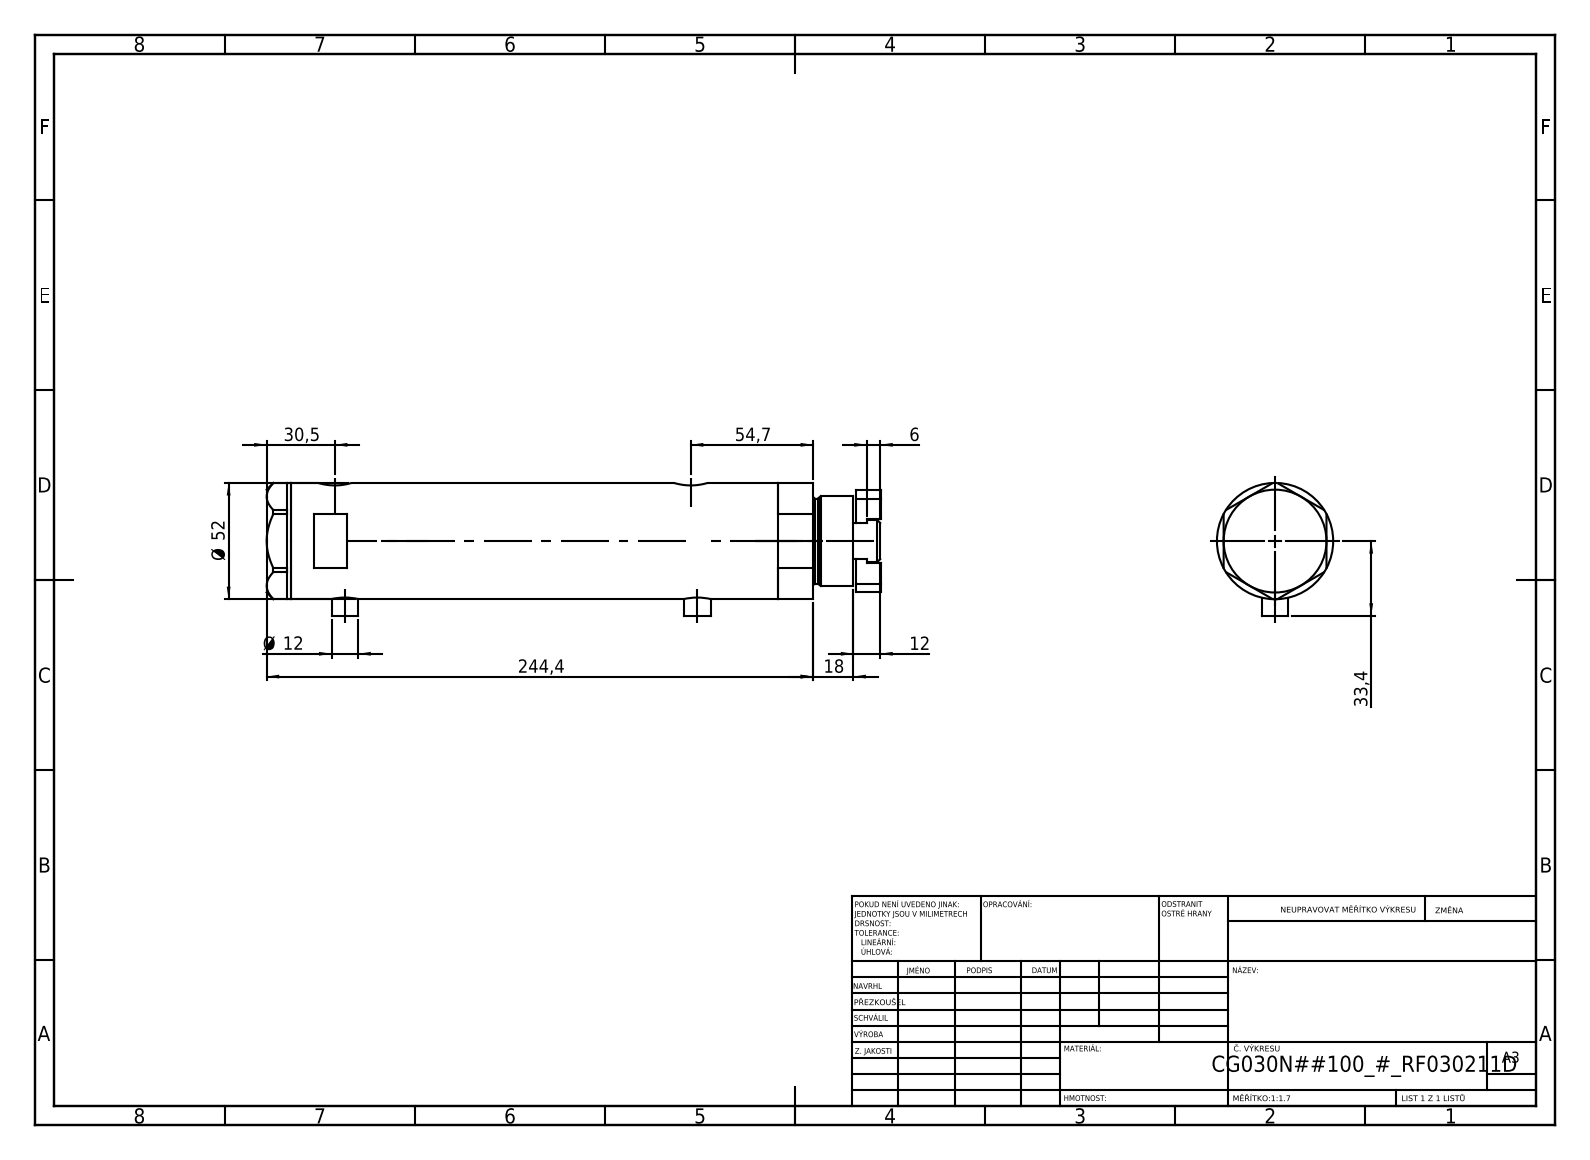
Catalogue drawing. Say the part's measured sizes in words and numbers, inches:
The part is named "V270CG_RF211D; V270CG_FRONT; V270CG_VC; V270CG_MIDDLE (+1 more)". Its 3-D file was written by "SolidWorks 2019 (CONFIG_CONTROL_DESIGN)". It is 6 solids with 174 faces: 89 planar, 65 cylindrical and 20 other. Overall it measures 10.811 by 2.339 by 2.047 inches. Its volume is 30.69 cubic inches and its surface area 170.5 square inches. Round holes: 4 of diameter 0.201, 4 of diameter 0.354, 2 of diameter 0.383, 2 of diameter 0.492, 2 of diameter 0.591, 1 of diameter 0.256, 1 of diameter 0.787, 1 of diameter 0.846, 1 of diameter 1.181, 1 of diameter 1.299, 1 of diameter 1.732. Round bosses or shafts: 2 of diameter 0.472, 1 of diameter 2.047, 1 of diameter 1.575, 1 of diameter 1.496, 1 of diameter 0.748. The main face-to-face distances are 0.433, 7.146, 0.937, 6.209, 1.37, 7.579, 1.811, 1.319, 9.012, 8.579. The hole center spacings are 0.659, 0.394, 1.258, 1.319, 0.114, 0.177, 6.091, 6.205.
